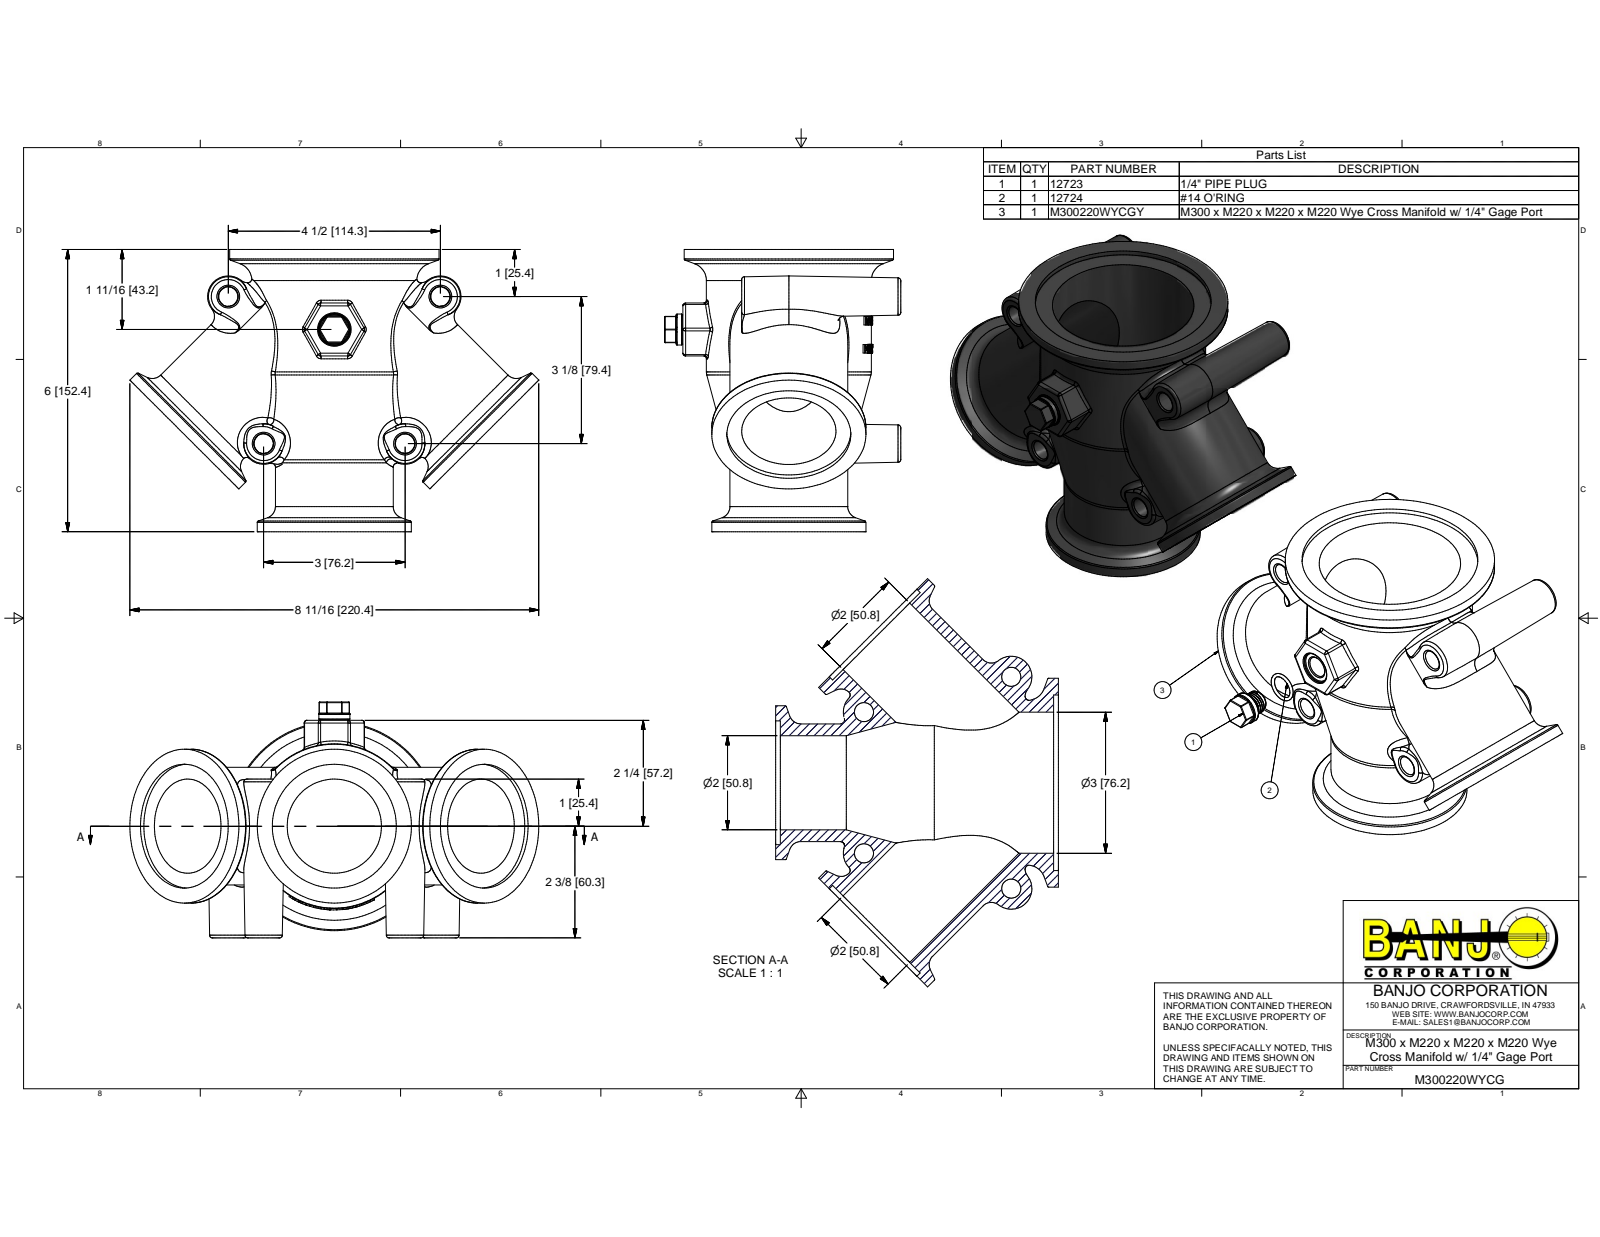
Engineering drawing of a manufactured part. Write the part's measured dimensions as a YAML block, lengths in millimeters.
part_name: "M300220WYCGX; M300220WYCGY; 12723; 12724 (+1 more)"
step_written_by: "Autodesk Inventor 2014 (AUTOMOTIVE_DESIGN)"
units: millimeters
bodies: {solids: 3, faces: 831, planar: 284, cylindrical: 117, other: 430}
overall_size: [220.38, 152.4, 127.32]
volume: 477749
surface_area: 154557
round_holes:
  - {diameter: 50.8, count: 3}
  - {diameter: 66.8, count: 3}
  - {diameter: 6.1, count: 1}
  - {diameter: 10.72, count: 1}
  - {diameter: 17.27, count: 1}
  - {diameter: 76.2, count: 1}
  - {diameter: 94.74, count: 1}
round_bosses_or_shafts:
  - {diameter: 83.06, count: 3}
  - {diameter: 63.5, count: 3}
  - {diameter: 112.78, count: 1}
  - {diameter: 88.9, count: 1}
  - {diameter: 16.76, count: 1}
  - {diameter: 13.46, count: 1}
partial_cylinders:
  - {radius: 0.38, count: 18}
  - {radius: 1.52, count: 12}
  - {radius: 45.21, count: 1}
face_to_face_distances: [2.54, 149.86, 152.4, 147.32, 28.58, 85.72, 117.47, 31.75, 7.18, 21.4]
